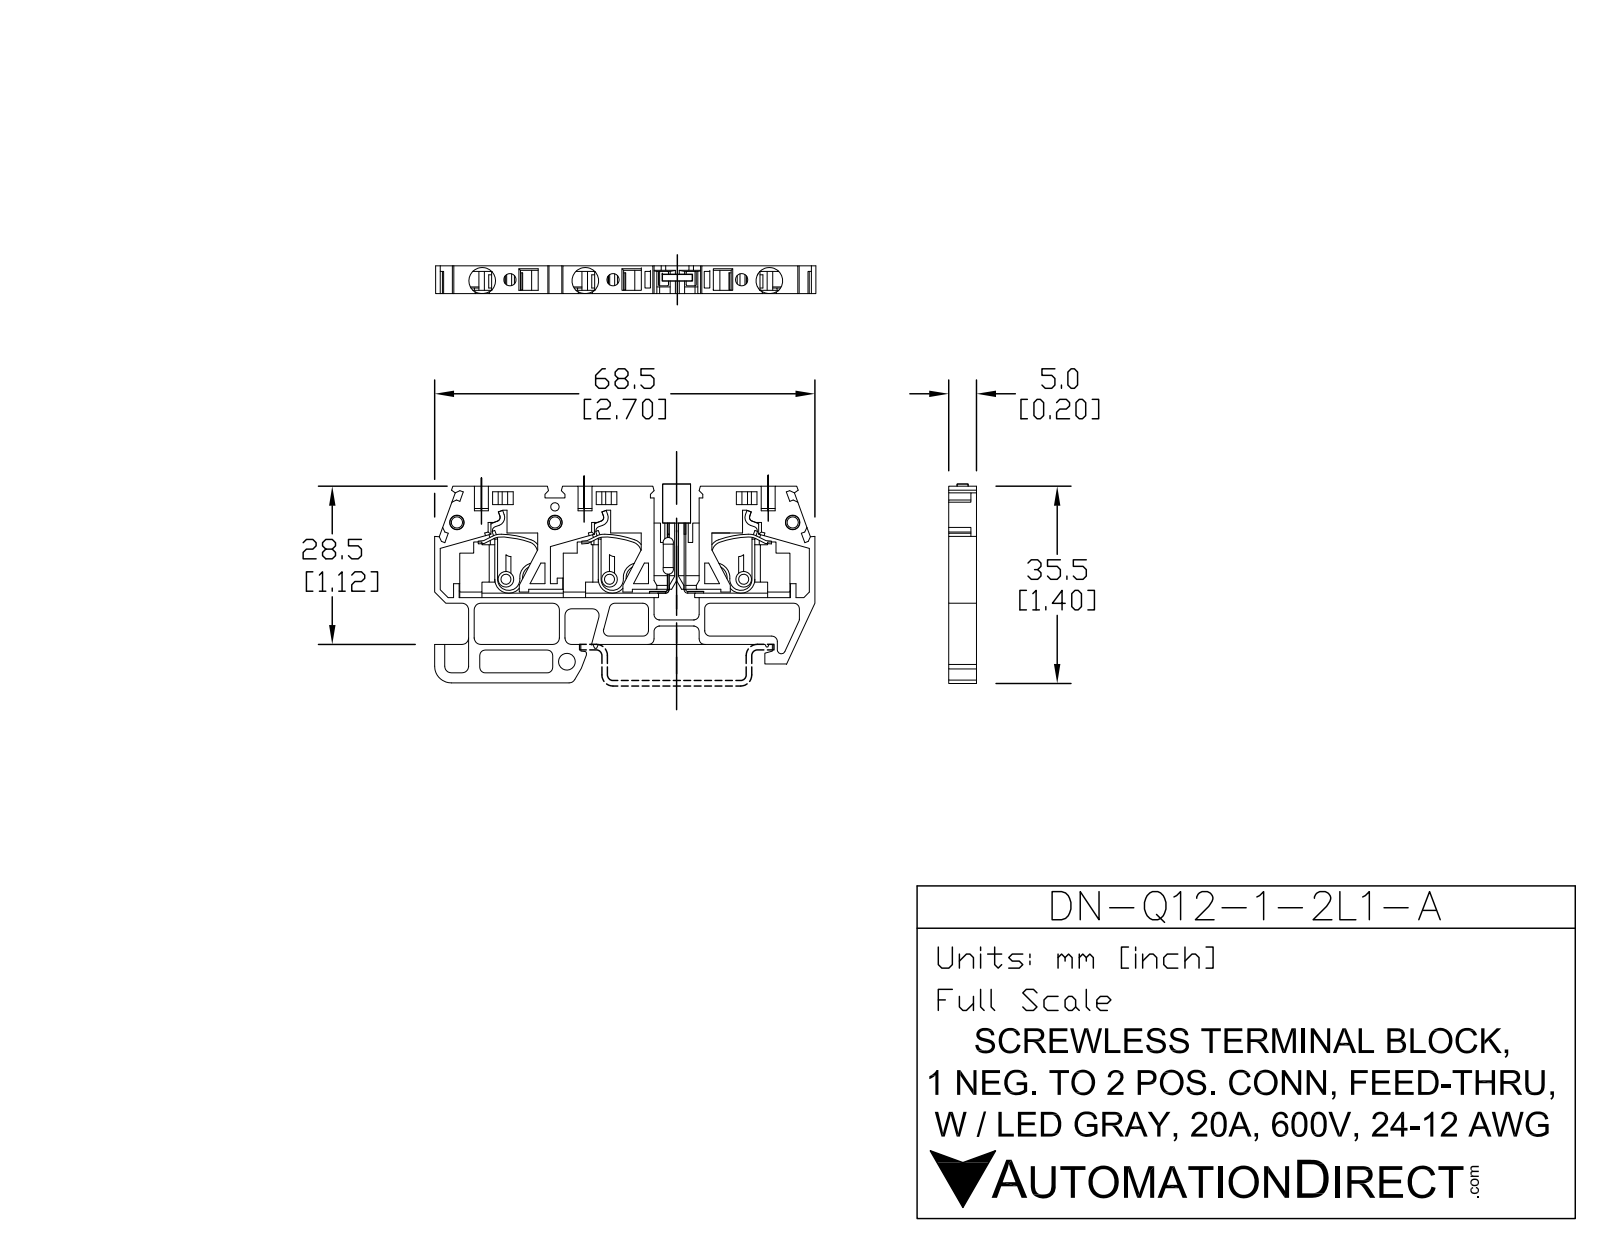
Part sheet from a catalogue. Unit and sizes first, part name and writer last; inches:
Units: inches
Overall size (bounding box): 2.701 × 1.409 × 0.22
Round holes (diameter × count): ⌀0.087 ×3, ⌀0.102 ×3, ⌀0.189 ×3, ⌀0.059 ×1, ⌀0.118 ×1
Round bosses / shafts (diameter × count): ⌀0.012 ×4, ⌀0.071 ×1
Partial cylindrical surfaces — rounded edges, fillets, slot ends (radius × count): R0.039 ×19, R0.047 ×12, R0.012 ×1, R0.028 ×1, R0.118 ×1
Main face-to-face distances: 0.197, 0.039, 0.079, 0.118, 0.193, 0.047, 0.331, 0.031, 0.071, 0.028
Hole centre spacings: 0.197, 0.732, 1.11, 1.843, 0.11, 0.535, 0.693, 0.702
Volume: 0.4 in³ · Surface area: 11.21 in²
Bodies: 5 solids, 415 faces (297 planar, 86 cylindrical, 32 other)
Part name (STEP PRODUCT): 42413D8_DN-Q12-1-2L1-A; 42413D6_DN-Q12-1-2DR-A; 20634 D8_20634 LN; 20631_Piega1 D8
STEP written by: SolidWorks 2013 (AUTOMOTIVE_DESIGN)
